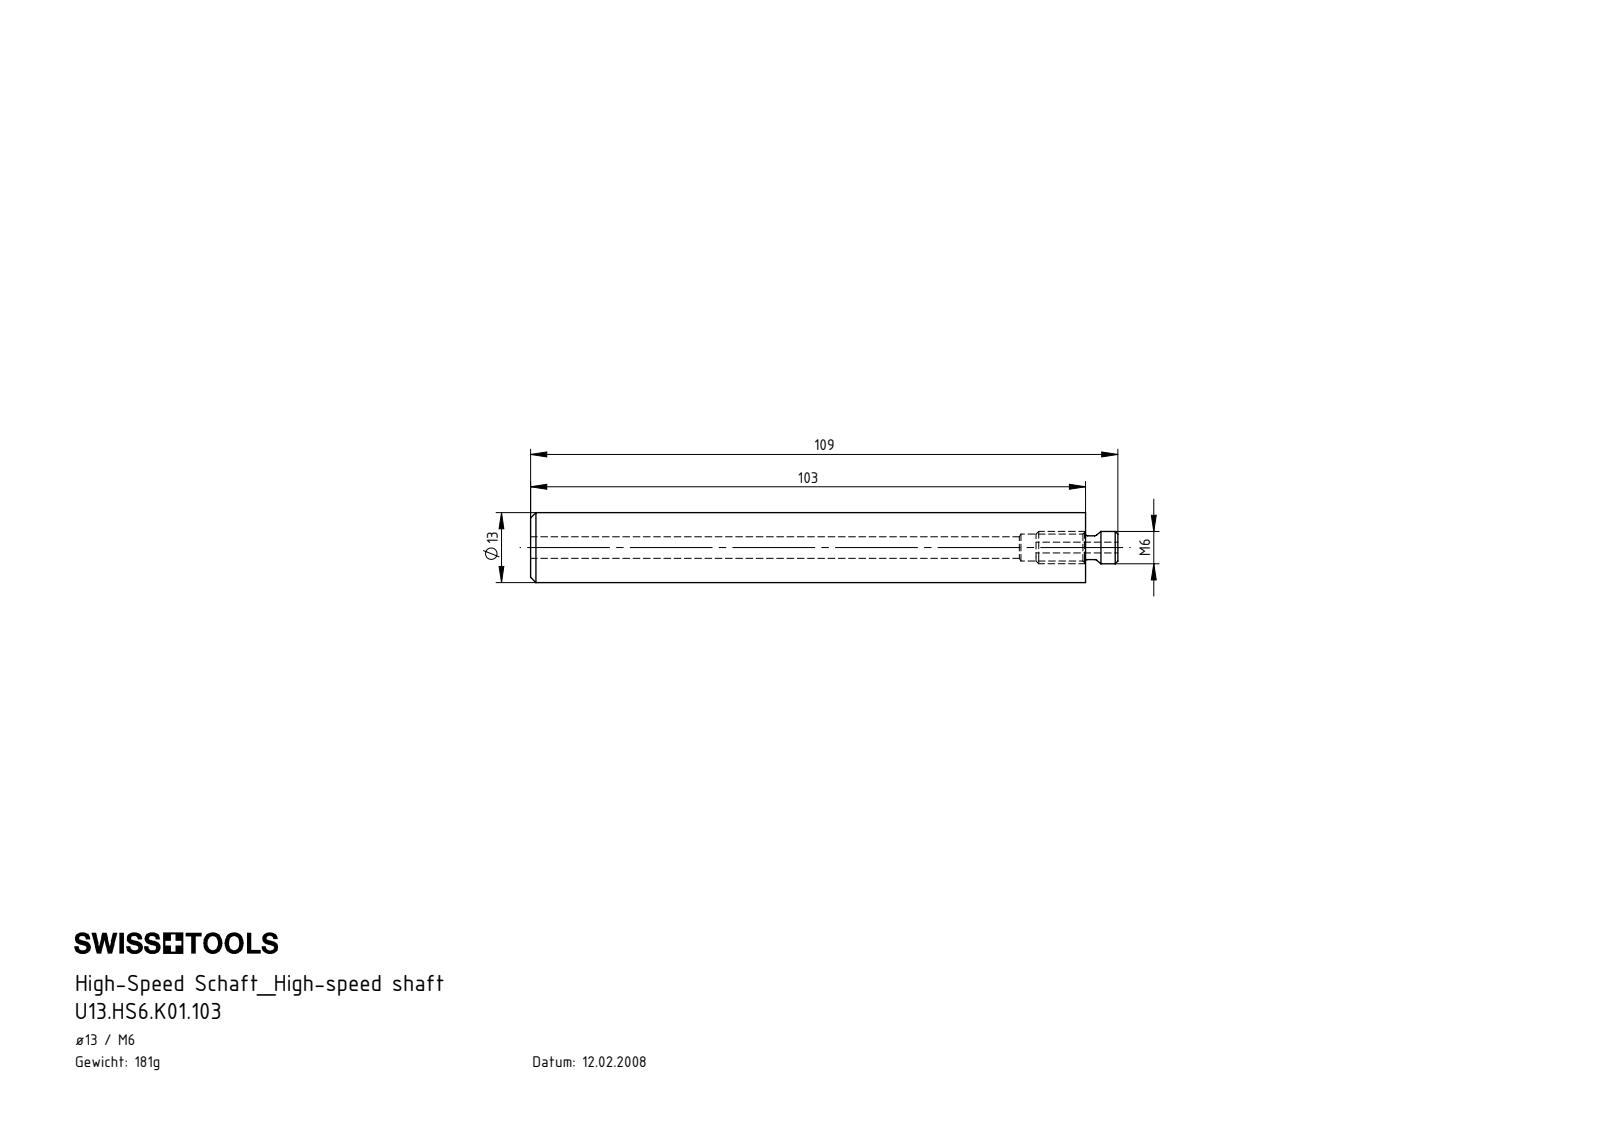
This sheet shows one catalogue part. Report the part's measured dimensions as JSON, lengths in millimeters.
{"part_name": "HM1-U13.001.103_A; HM1-BG1.006.015_A; U13.HS6.K01.103", "step_written_by": "SolidWorks 2017 (AUTOMOTIVE_DESIGN)", "units": "millimeters", "bodies": {"solids": 2, "faces": 20, "planar": 5, "cylindrical": 7, "other": 8}, "overall_size": [109, 13, 13], "volume_mm3": 12615, "surface_area_mm2": 6169, "round_holes": [[2, 1], [4, 1], [5, 1]], "round_bosses_or_shafts": [[13, 1], [6, 1], [4.4, 1]], "face_to_face_distances": [103, 93.8, 9.2, 109, 15.2, 6, 102.8, 9, 6.2]}
